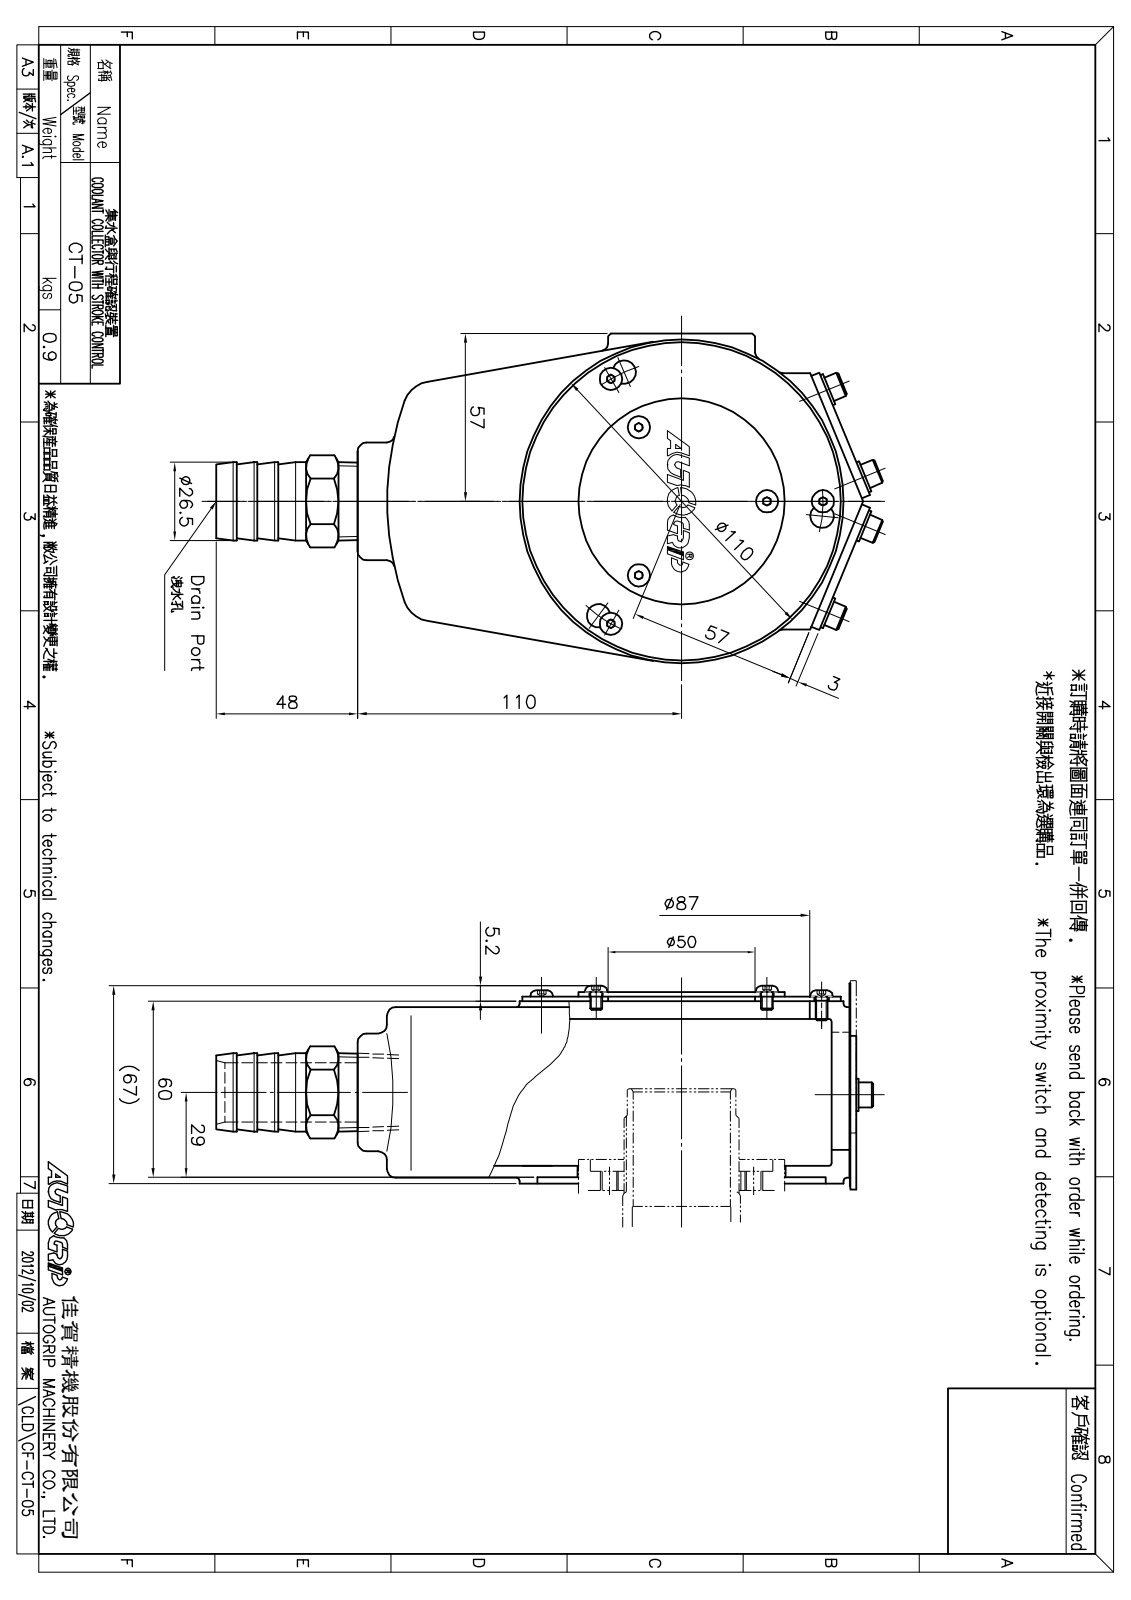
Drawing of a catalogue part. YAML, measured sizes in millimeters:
part_name: "CF-CT-05-12000; M5x10; CT-08洩油管; CT-05集水盒本體 (+1 more)"
step_written_by: "SolidWorks 2016 (CONFIG_CONTROL_DESIGN)"
units: millimeters
bodies: {solids: 11, faces: 363, planar: 164, cylindrical: 124, other: 75}
overall_size: [229.76, 112, 70]
volume: 250962
surface_area: 135584
round_holes:
  - {diameter: 5, count: 4}
  - {diameter: 5.5, count: 4}
  - {diameter: 3.3, count: 3}
  - {diameter: 12, count: 2}
  - {diameter: 25, count: 1}
  - {diameter: 70.5, count: 1}
  - {diameter: 87, count: 1}
round_bosses_or_shafts:
  - {diameter: 8.5, count: 4}
  - {diameter: 5, count: 4}
  - {diameter: 110, count: 1}
  - {diameter: 109, count: 1}
  - {diameter: 40, count: 1}
  - {diameter: 33, count: 1}
partial_cylinders:
  - {radius: 2.75, count: 16}
  - {radius: 3, count: 10}
  - {radius: 7, count: 8}
  - {radius: 2, count: 6}
  - {radius: 2.5, count: 5}
  - {radius: 4, count: 3}
  - {radius: 6, count: 2}
  - {radius: 10, count: 2}
face_to_face_distances: [4, 56, 2, 6, 1.5, 60, 54, 57.5, 0.5, 63.5]
hole_center_spacings: [41.49, 58.68, 48, 83.14, 13.34, 15.75, 16.25, 32]
